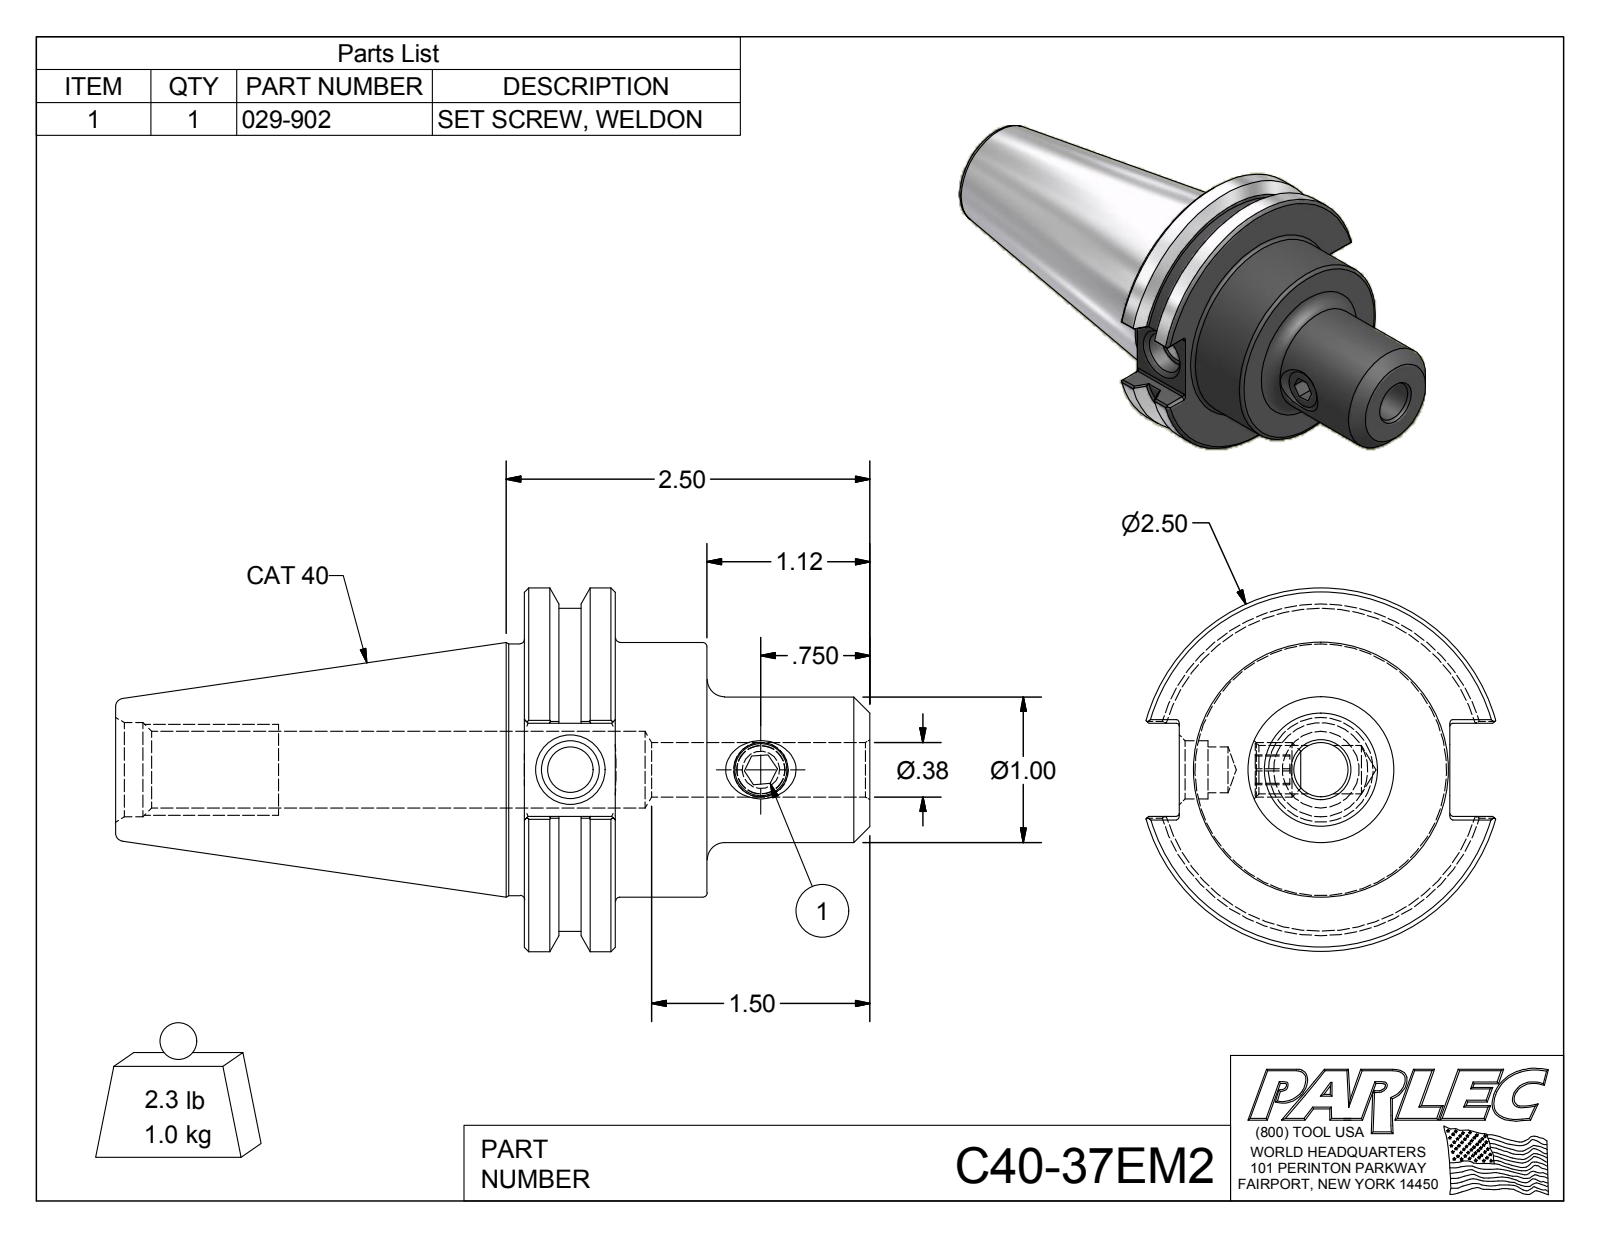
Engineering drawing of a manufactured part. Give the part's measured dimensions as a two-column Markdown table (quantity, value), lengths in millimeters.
| quantity | value |
| --- | --- |
| part name | C40-37EM2; C40-37EM2-1; 029-902 |
| STEP written by | Autodesk Inventor 2012 (AUTOMOTIVE_DESIGN) |
| units | millimeters |
| bodies | 2 solids, 104 faces (41 planar, 29 cylindrical, 34 other) |
| overall size | 131.7 × 63.5 × 61.1 |
| volume | 135 600 mm³ |
| surface area | 26 480 mm² |
| round holes (diameter × count) | 8 × 1, 8.4 × 1, 9.5 × 1, 10.1 × 1, 13.4 × 1, 16.5 × 1 |
| round bosses / shafts (diameter × count) | 63.5 × 1, 56.4 × 1, 44.5 × 1, 43.9 × 1, 25.4 × 1, 9.5 × 1 |
| partial cylindrical surfaces (radius × count) | 0.5 × 12 |
| main face-to-face distances | 15.9, 31.9, 16, 60.3, 44.5, 28.4, 16.3, 6, 47.2, 71.4 |
| hole center spacings | 33.3 |
